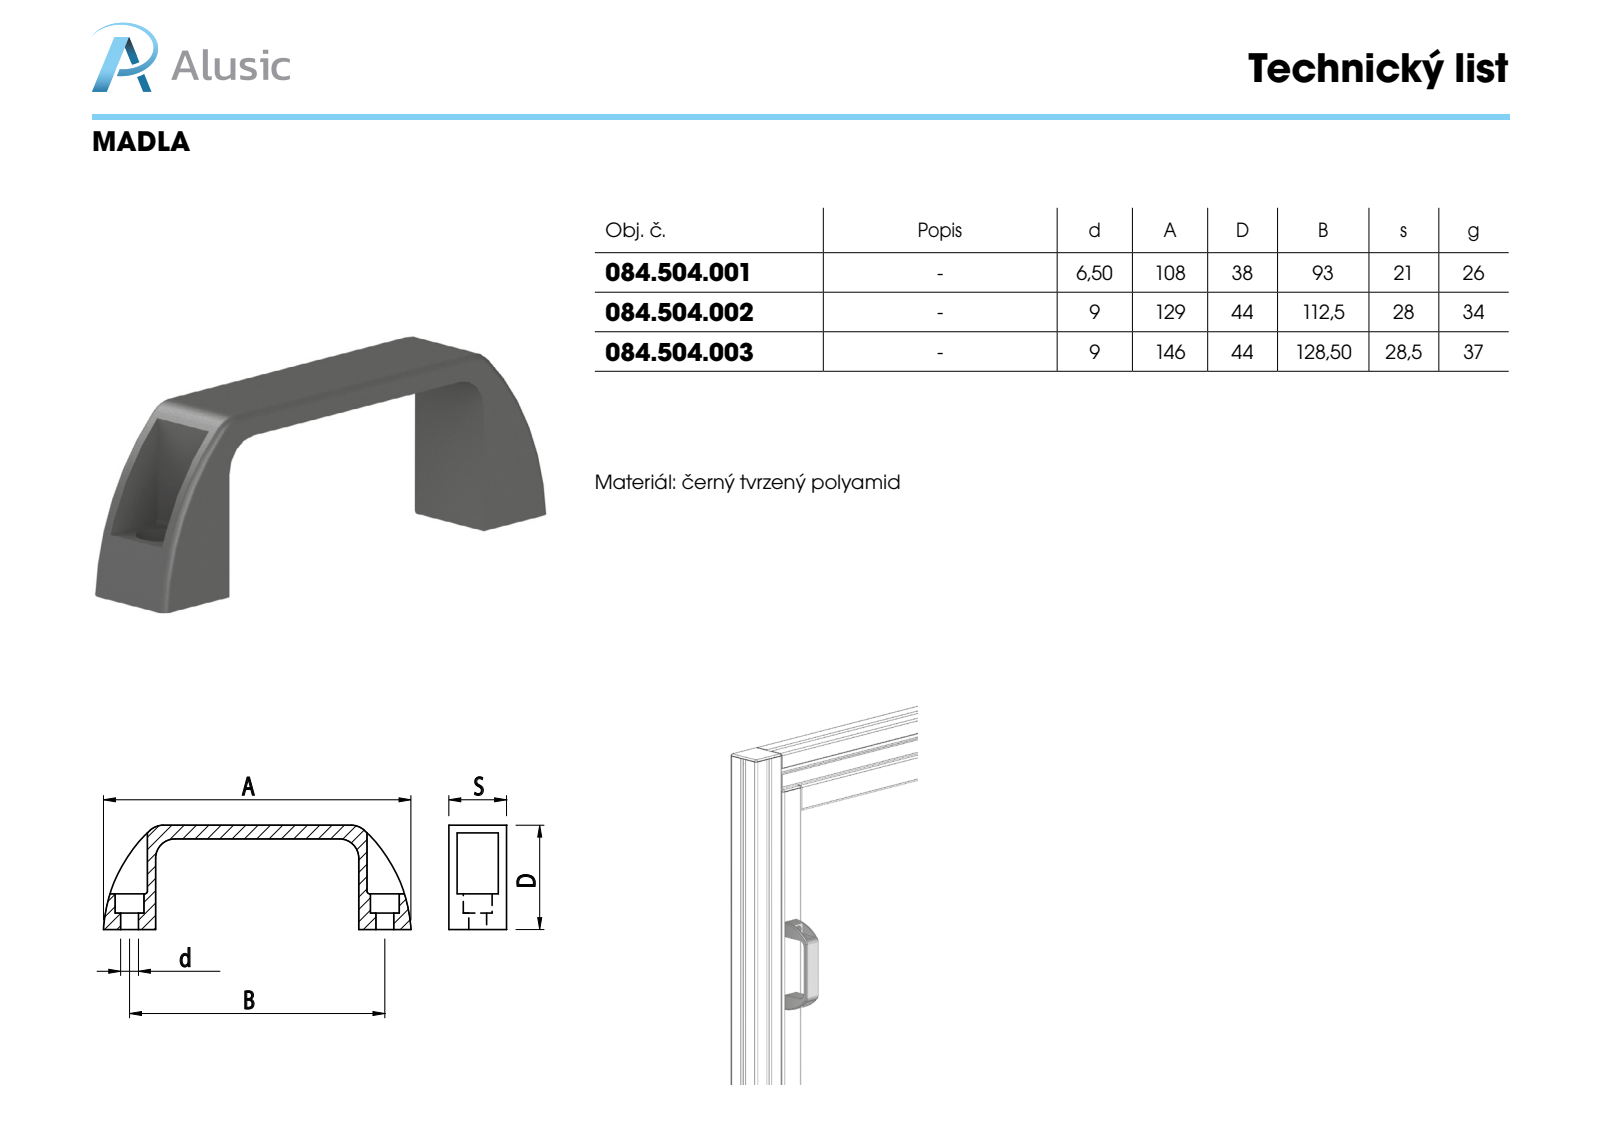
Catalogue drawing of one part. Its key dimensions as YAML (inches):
part_name: "084.504.001"
step_written_by: "SolidWorks 2011 (CONFIG_CONTROL_DESIGN)"
units: inches
bodies: {solids: 1, faces: 51, planar: 18, cylindrical: 23, other: 10}
overall_size: [4.409, 1.496, 0.827]
volume: 1.301
surface_area: 16.96
round_holes:
  - {diameter: 0.256, count: 2}
  - {diameter: 0.413, count: 2}
partial_cylinders:
  - {radius: 0.059, count: 6}
  - {radius: 0.276, count: 4}
  - {radius: 0.039, count: 2}
  - {radius: 2.118, count: 2}
face_to_face_distances: [0.118, 0.197, 0.827, 0.709, 1.299, 1.496, 3.031, 2.913, 0.591, 3.15]
hole_center_spacings: [3.661]
